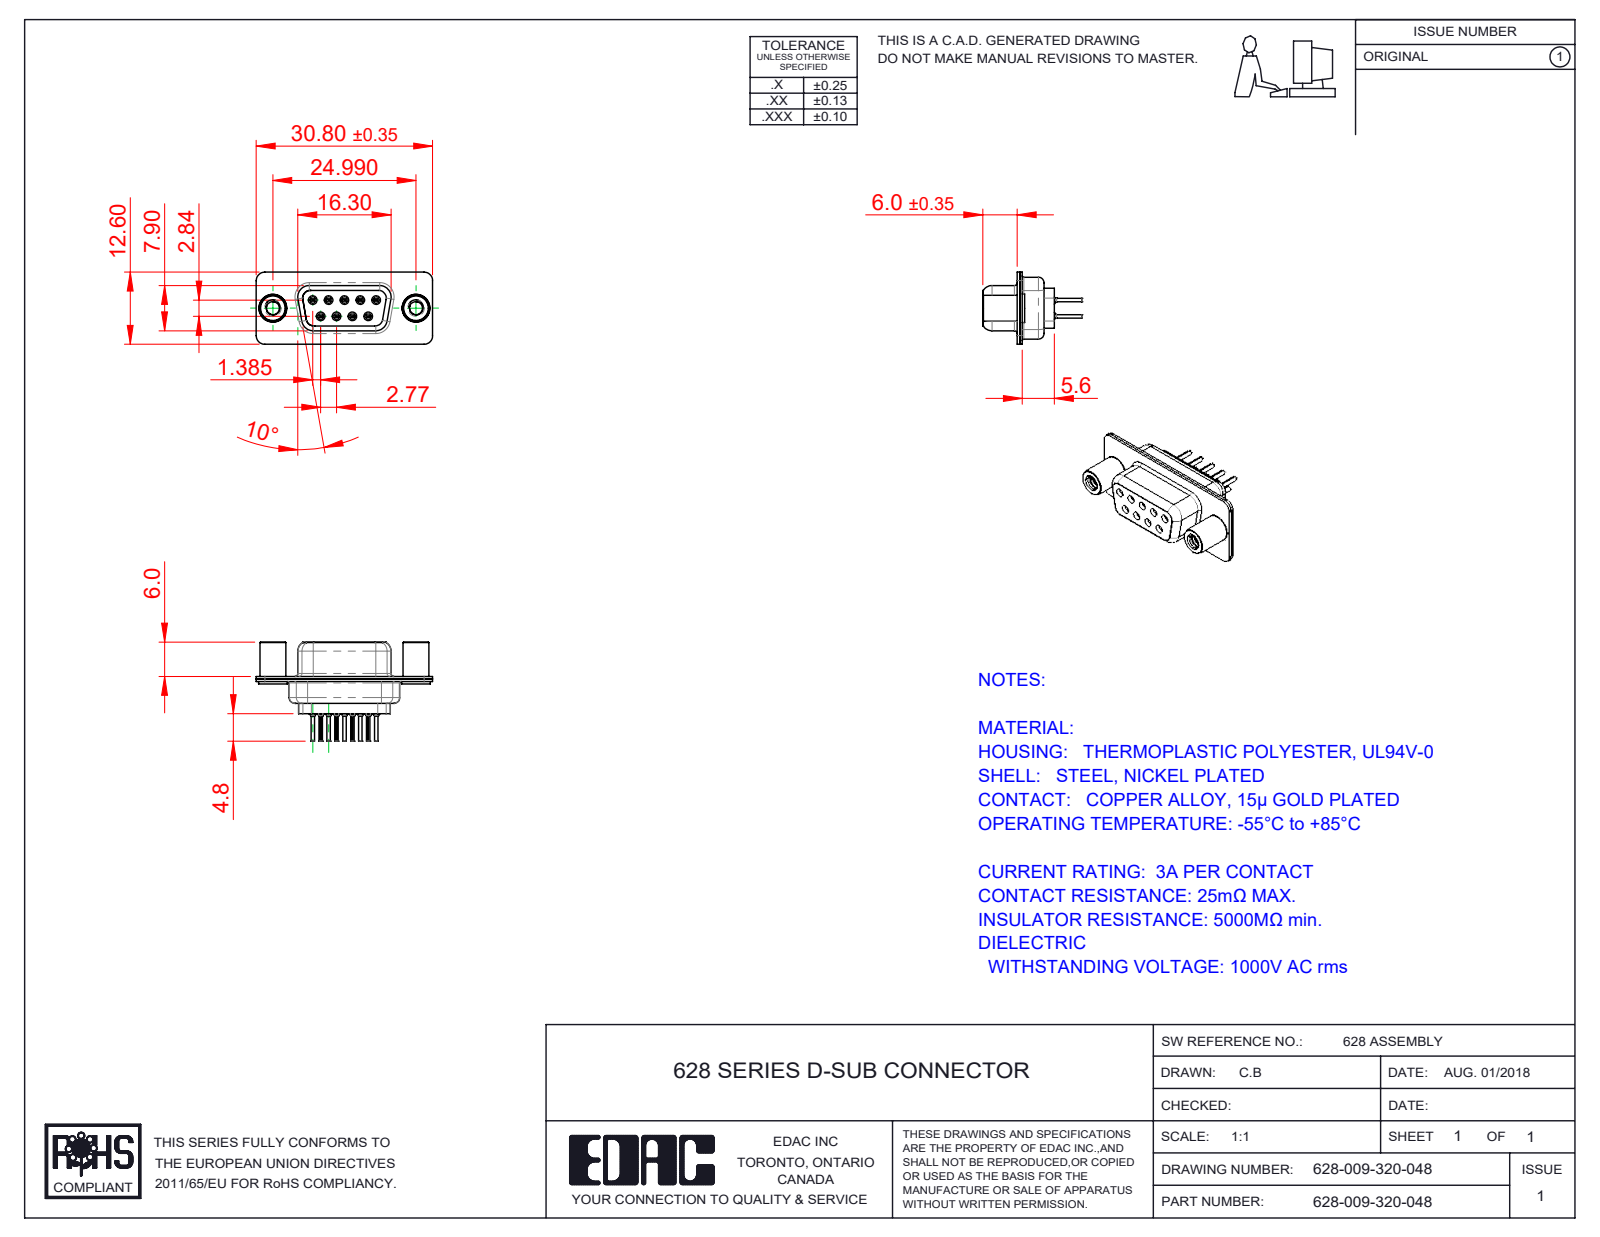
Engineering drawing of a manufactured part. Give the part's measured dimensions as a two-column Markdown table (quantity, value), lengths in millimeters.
| quantity | value |
| --- | --- |
| part name | 628 Housing_09 LP; 628 4-40 Threaded Standoff; 628 Shell Rear_09 Contacts; 628 Shell Front_09 Contacts (+3 more) |
| STEP written by | SolidWorks 2020 (CONFIG_CONTROL_DESIGN) |
| units | millimeters |
| bodies | 14 solids, 1456 faces (348 planar, 462 cylindrical, 646 other) |
| overall size | 30.8 × 17.3 × 12.6 |
| volume | 1 823 mm³ |
| surface area | 4 707 mm² |
| round holes (diameter × count) | 0.2 × 9, 0.8 × 9, 0.9 × 9, 1.1 × 9, 1.6 × 9, 1.7 × 5, 2.26 × 2, 4 × 2, 4.05 × 2, 4.85 × 2 |
| round bosses / shafts (diameter × count) | 2 × 9, 1.5 × 9, 1.2 × 9, 0.6 × 9, 5 × 2, 4.95 × 2, 4.8 × 2, 4.5 × 2 |
| partial cylindrical surfaces (radius × count) | 0.1 × 18, 1.5 × 17, 2 × 12, 0.28 × 9, 1.35 × 6, 0.25 × 4, 0.5 × 4, 0.6 × 4 |
| main face-to-face distances | 0.45, 0.4, 0.9, 1.9, 8.5, 6.6, 1.4, 0.85, 1.8, 0.5 |
| hole center spacings | 3.16, 2.77, 5.54, 5.03, 5.04, 8.31, 7.48, 7.49 |
